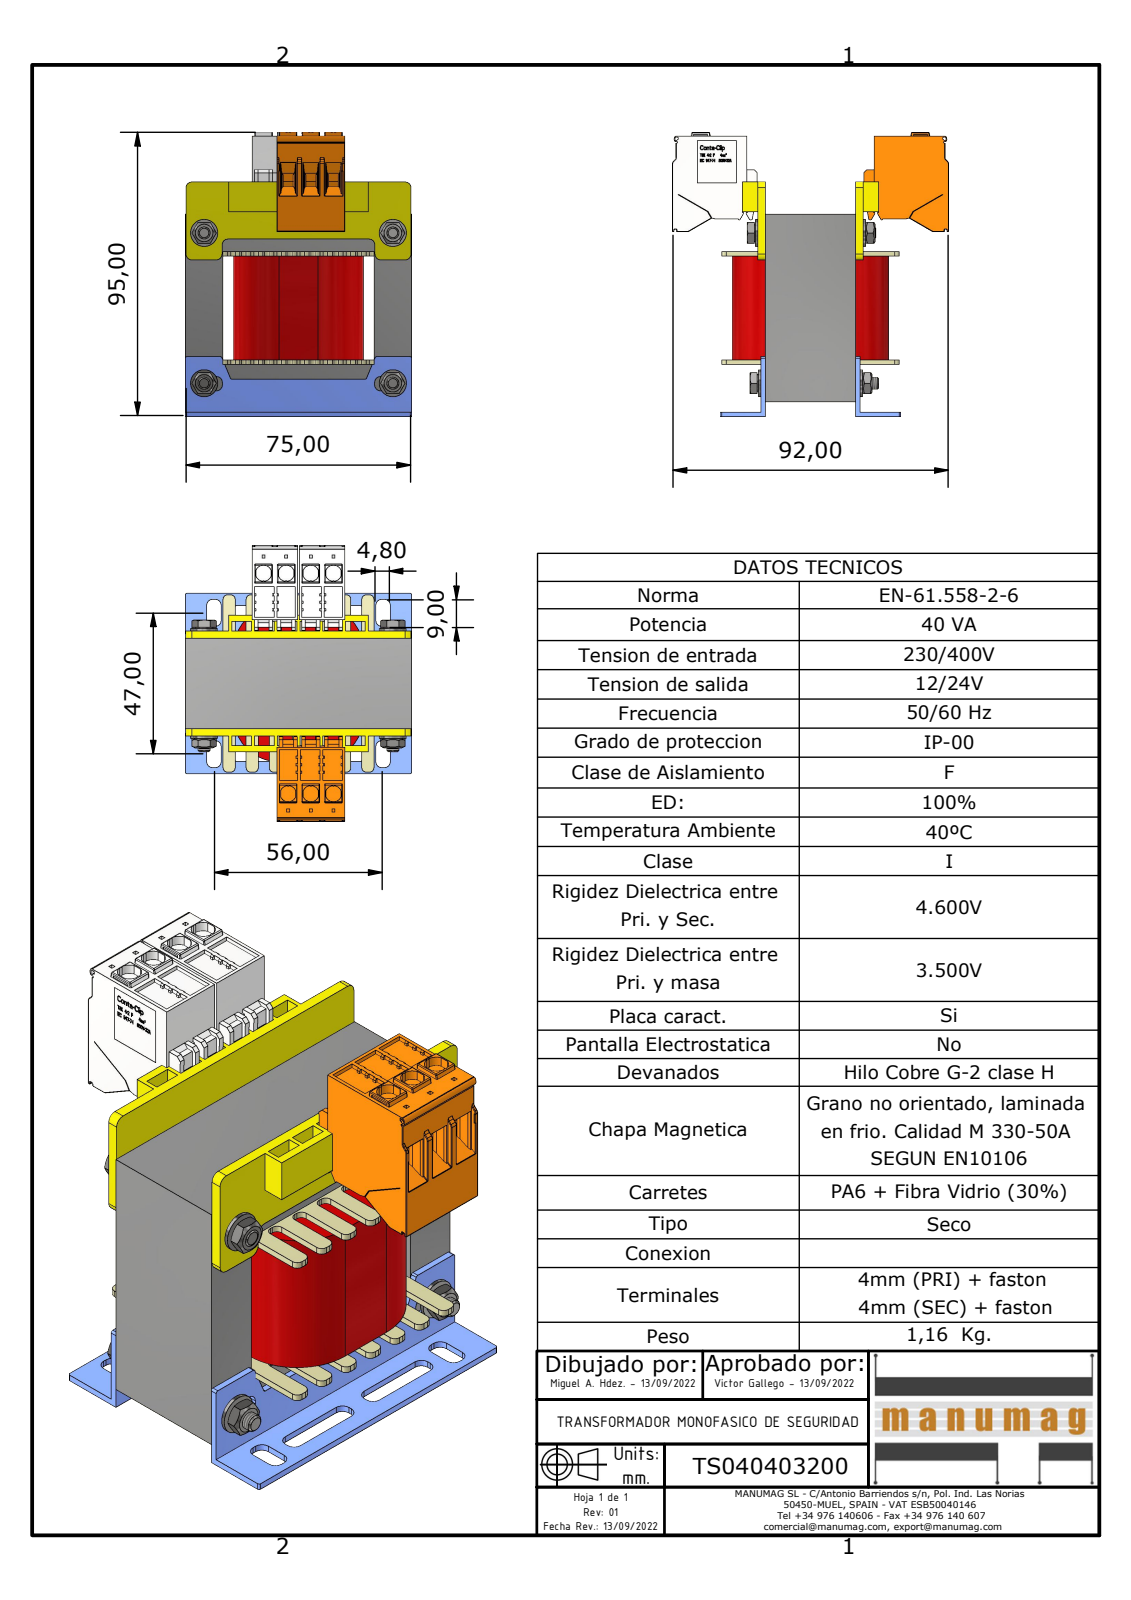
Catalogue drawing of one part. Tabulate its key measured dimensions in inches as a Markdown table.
| quantity | value |
| --- | --- |
| part name | TS040403200; EI75 x 62,5 - 30 (RC25); AF25DIN; EI 75 X 62,5 - 30 (+6 more) |
| STEP written by | Autodesk Inventor 2023 (AUTOMOTIVE_DESIGN) |
| units | inches |
| bodies | 25 solids, 5918 faces (4734 planar, 821 cylindrical, 363 other) |
| overall size | 3.726 × 3.618 × 2.953 |
| volume | 12.64 in³ |
| surface area | 130.3 in² |
| round holes (diameter × count) | 0.128 × 4, 0.169 × 4, 0.177 × 4, 0.157 × 2 |
| round bosses / shafts (diameter × count) | 0.354 × 4, 0.232 × 4, 0.143 × 4, 0.157 × 2 |
| partial cylindrical surfaces (radius × count) | 0.006 × 259, 0.008 × 81, 0.059 × 52, 0.079 × 48, 0.02 × 32, 0.012 × 12, 0.039 × 8, 0.106 × 7 |
| main face-to-face distances | 0.492, 1.969, 1.181, 0.984, 0.059, 1.476, 2.461, 1.339, 0.098, 1.28 |
| hole center spacings | 1.969, 2.461, 3.151 |
